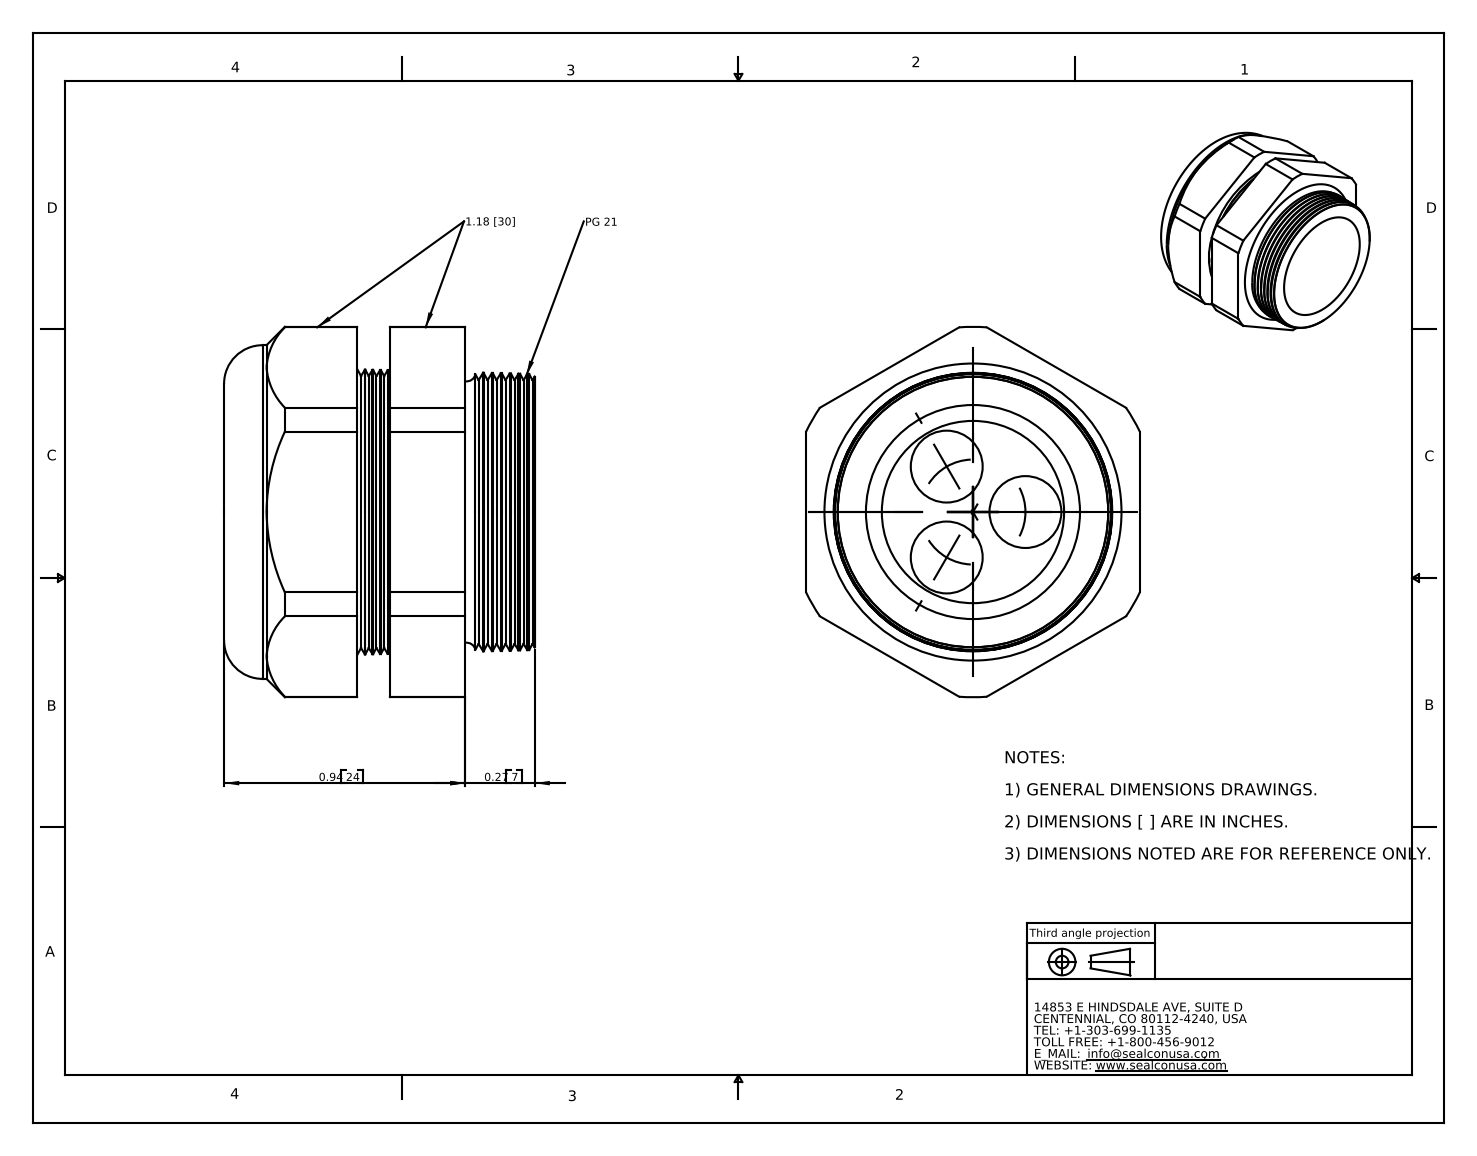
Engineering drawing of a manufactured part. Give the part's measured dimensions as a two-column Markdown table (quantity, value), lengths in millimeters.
| quantity | value |
| --- | --- |
| part name | CD21A2-BR |
| STEP written by | SolidWorks 2007 (CONFIG_CONTROL_DESIGN) |
| units | millimeters |
| bodies | 2 solids, 126 faces (20 planar, 26 cylindrical, 80 other) |
| overall size | 36.7 × 33 × 30.7 |
| volume | 16 850 mm³ |
| surface area | 8 813 mm² |
| round holes (diameter × count) | 7.1 × 3, 17.5 × 1, 18 × 1 |
| round bosses / shafts (diameter × count) | 33 × 1 |
| partial cylindrical surfaces (radius × count) | 18.3 × 1 |
| main face-to-face distances | 33, 3.2, 13.2, 16.4, 23.9, 10.7, 7.5, 30.7, 17.5, 14.4 |
| hole center spacings | 9, 5.2, 5.2 |
